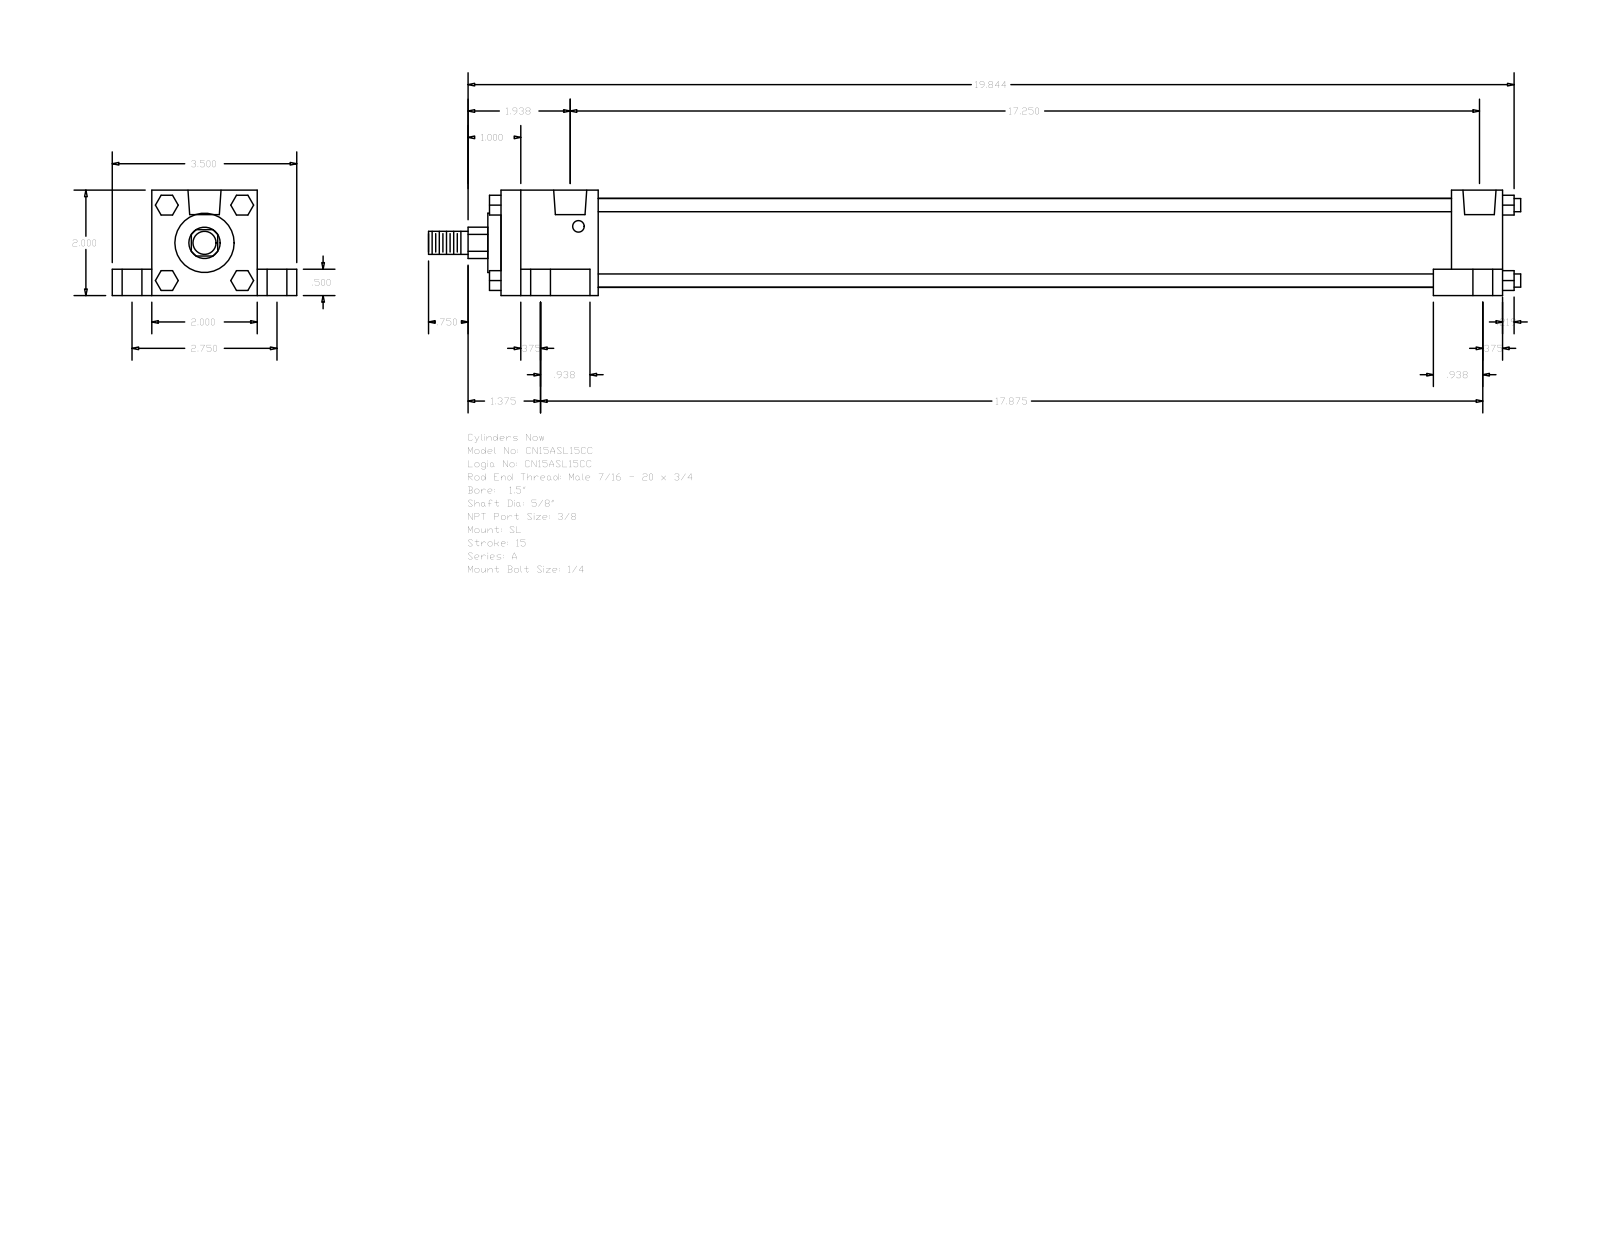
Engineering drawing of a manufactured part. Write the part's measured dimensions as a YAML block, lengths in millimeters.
part_name: "A_SL__0150_0.625"
step_written_by: "GSSL Pune (CONFIG_CONTROL_DESIGN)"
units: millimeters
bodies: {solids: 0, faces: 148, planar: 112, cylindrical: 36, other: 0}
overall_size: [526.26, 88.9, 50.8]
round_holes:
  - {diameter: 5.56, count: 4}
  - {diameter: 9.53, count: 4}
  - {diameter: 15.88, count: 4}
  - {diameter: 15.93, count: 2}
round_bosses_or_shafts:
  - {diameter: 6.35, count: 4}
  - {diameter: 42.93, count: 1}
  - {diameter: 28.57, count: 1}
  - {diameter: 15.88, count: 1}
  - {diameter: 11.11, count: 1}
partial_cylinders:
  - {radius: 7.54, count: 1}
face_to_face_distances: [50.8, 19.05, 38.1, 12.7, 69.85, 482.6, 9.52, 33.34, 457.99, 24.61]
hole_center_spacings: [3.97, 34.96, 35.36, 37.73, 39.41, 69.84, 430.21, 434.18]
